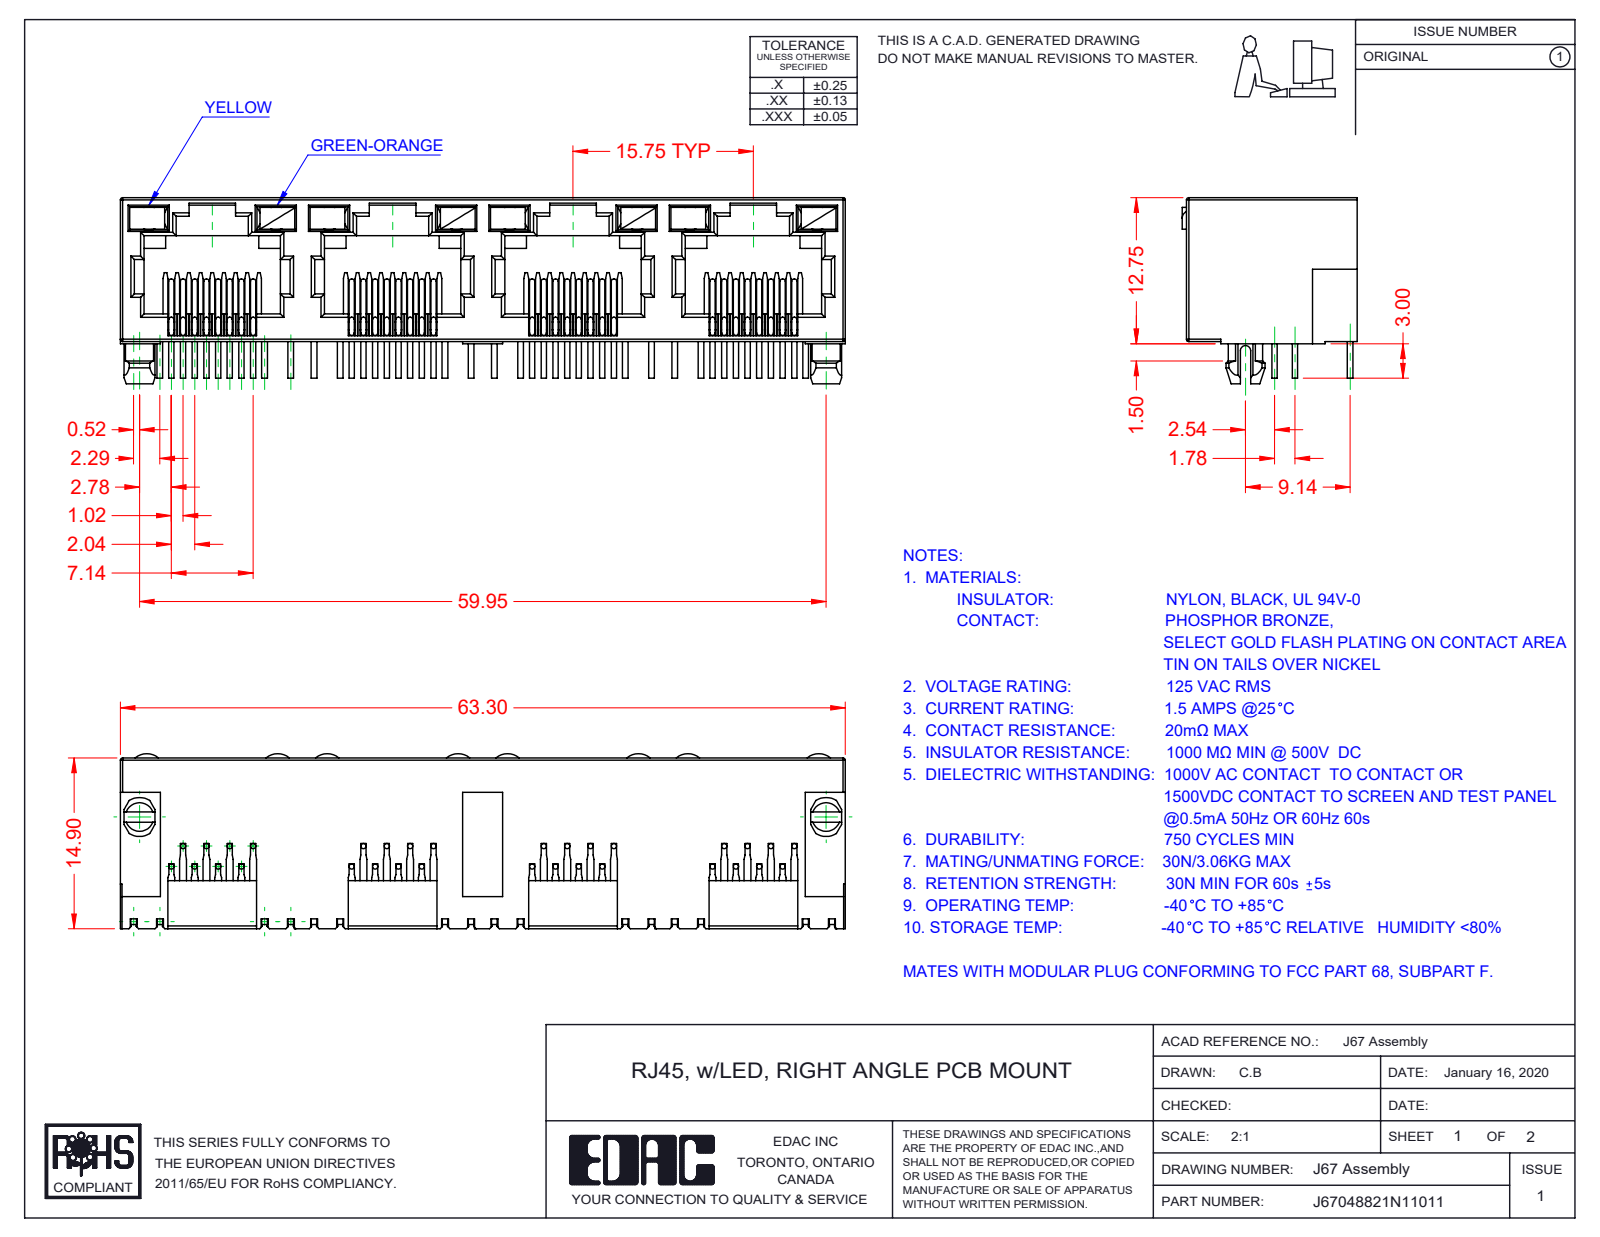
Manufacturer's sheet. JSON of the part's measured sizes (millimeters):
{"part_name": "67 LED RH_7-Green-Orange; 67 LED LH_1-Yellow; 67 Contacts; 67 Insulator (+1 more)", "step_written_by": "SolidWorks 2016 (CONFIG_CONTROL_DESIGN)", "units": "millimeters", "bodies": {"solids": 41, "faces": 2473, "planar": 1781, "cylindrical": 484, "other": 208}, "overall_size": [63.3, 16.25, 15.28], "volume_mm3": 5159, "surface_area_mm2": 11573, "round_bosses_or_shafts": [[0.46, 96]], "partial_cylinders_radius": [[0.2, 66], [0.3, 29], [0.45, 9], [1.55, 8], [1.5, 2], [1.7, 2], [0.35, 1], [1, 1]], "face_to_face_distances": [0.5, 12.55, 1.89, 0.89, 10, 15.75, 1, 1.39, 11, 11.89]}
